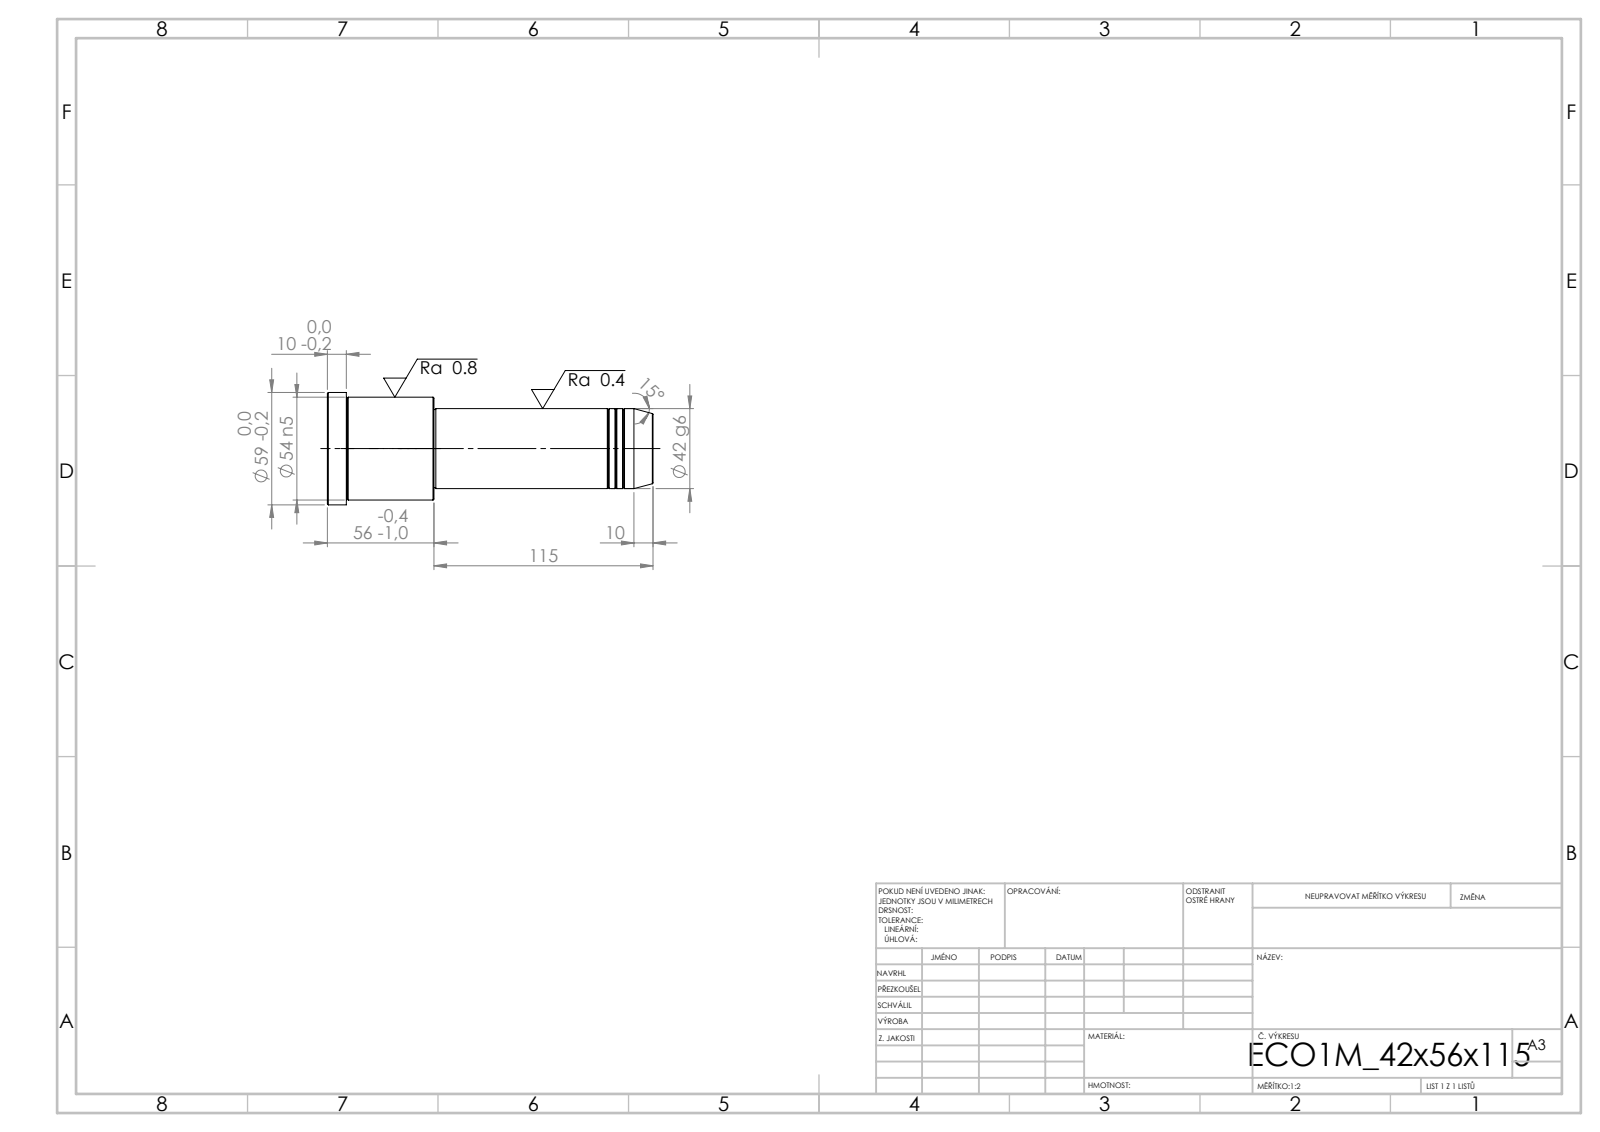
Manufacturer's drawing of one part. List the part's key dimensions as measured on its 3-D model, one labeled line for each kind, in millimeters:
STEP written by: SolidWorks 2019 (CONFIG_CONTROL_DESIGN)
Units: millimetres
Bodies: 1 solid, 43 faces (5 planar, 14 cylindrical, 24 other)
Overall size (bounding box): 171 × 59 × 59
Volume: 289 991 mm³ · Surface area: 30 247 mm²
Round bosses / shafts (diameter × count): ⌀59 ×1, ⌀54 ×1, ⌀42 ×1, ⌀41 ×1
Main face-to-face distances: 171, 115, 56, 161, 46, 10, 114, 1, 47, 57
